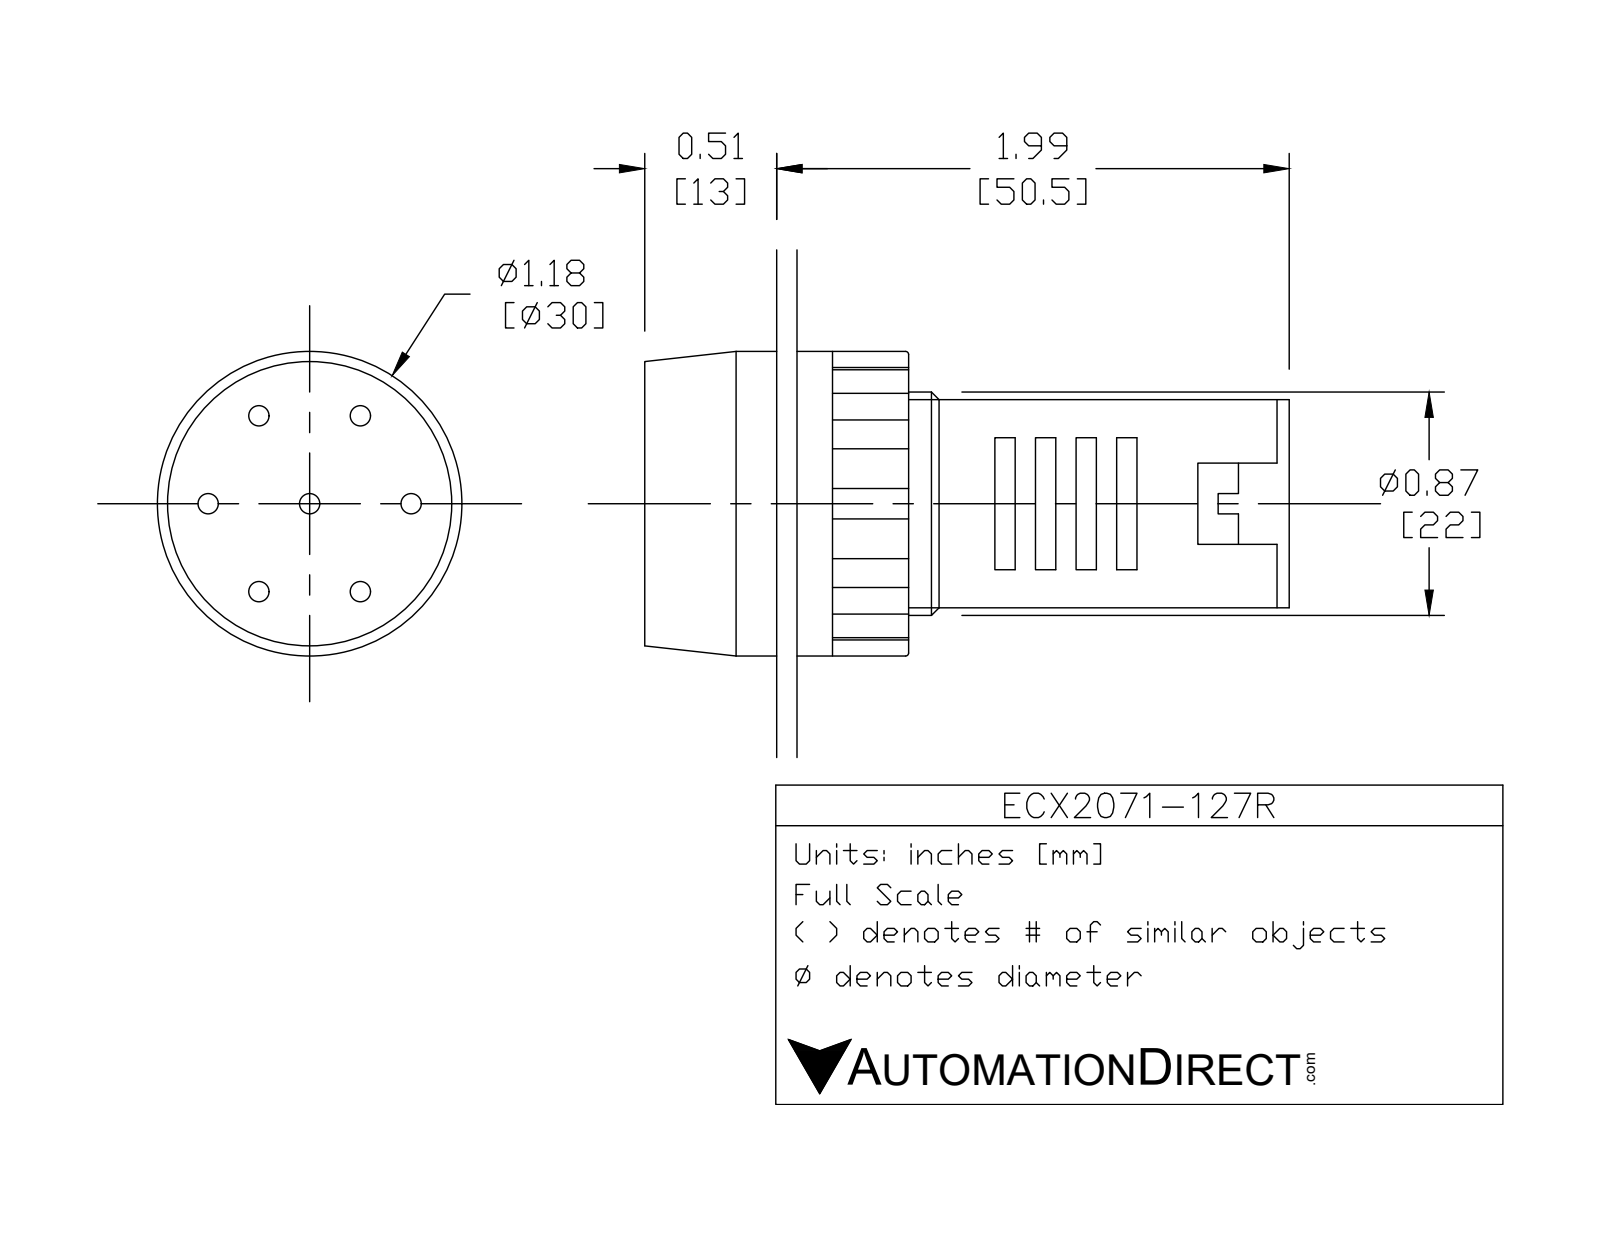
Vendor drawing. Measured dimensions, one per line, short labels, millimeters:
name: ECX2071-127
written by: SolidWorks 2017 (AUTOMOTIVE_DESIGN)
unit: mm
bodies: 6 solids, 196 faces (89 planar, 79 cylindrical, 28 other)
size: 63.5 × 30 × 30
volume: 26 255 mm³; area: 12 389 mm²
holes: 4× ⌀2, 2× ⌀5.5, 1× ⌀22, 1× ⌀22.5
bosses: 2× ⌀4, 1× ⌀30, 1× ⌀29, 1× ⌀26.5, 1× ⌀20
rounds: 22× R0.25, 8× R1, 1× R9
face distances: 2, 4, 6, 8, 10, 12, 12.5, 16, 0.5, 13
hole spacings: 7.48, 10, 13.66, 14.14, 4.62, 20, 9.24
